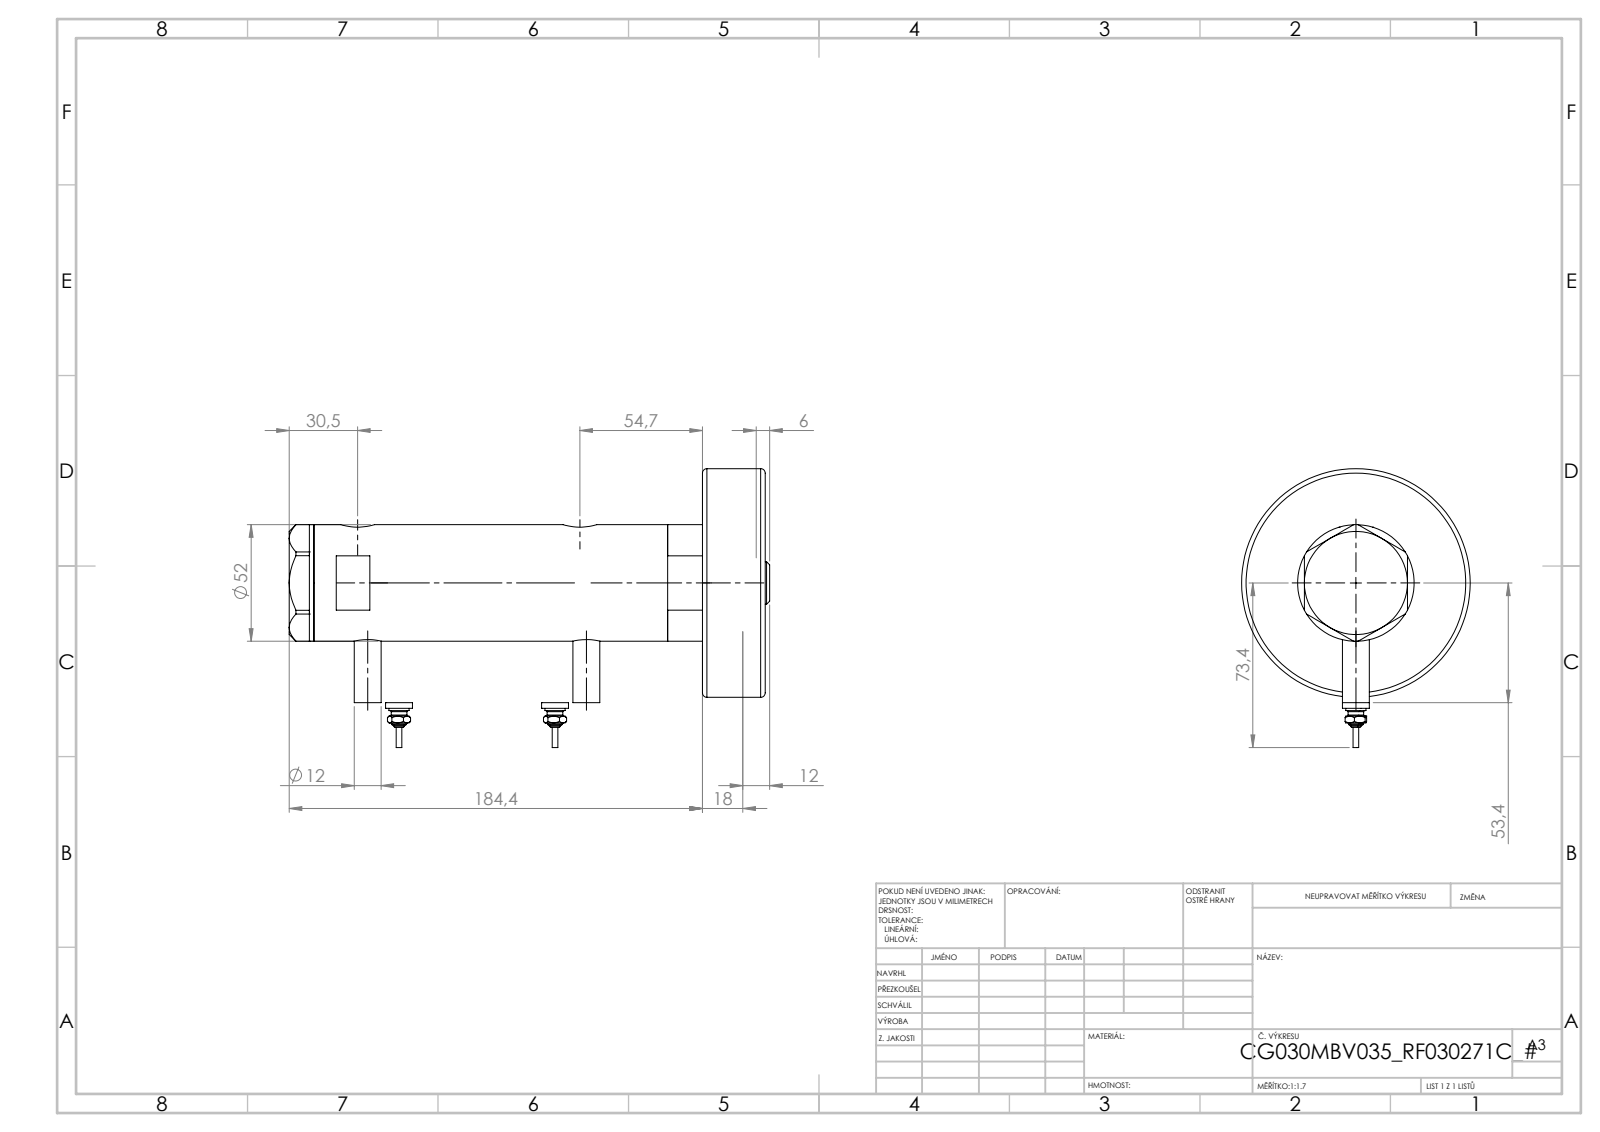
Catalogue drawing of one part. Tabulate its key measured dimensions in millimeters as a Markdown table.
| quantity | value |
| --- | --- |
| part name | V270CG_SWITCH; V270CG_BACK; V270CG_MIDDLE; V270CG_271C (+2 more) |
| STEP written by | SolidWorks 2019 (CONFIG_CONTROL_DESIGN) |
| units | millimeters |
| bodies | 7 solids, 256 faces (97 planar, 81 cylindrical, 78 other) |
| overall size | 184.02 × 109.3 × 102 |
| volume | 524 026 mm³ |
| surface area | 104 018 mm² |
| round holes (diameter × count) | 5 × 2, 9.73 × 2, 12.5 × 2, 15 × 2, 6.5 × 1, 20 × 1, 21.5 × 1, 30 × 1, 33 × 1, 40 × 1, 44 × 1 |
| round bosses / shafts (diameter × count) | 12 × 3, 9 × 2, 7 × 2, 4.34 × 2, 2.4 × 2, 102 × 1, 52 × 1, 38 × 1 |
| main face-to-face distances | 28, 140.46, 168.46, 51.9, 23.8, 116.66, 144.66, 11, 34.8, 151.46 |
| hole center spacings | 2.9, 4.5, 61.75, 64.65, 66.25, 69.15, 2.89, 2.91 |
